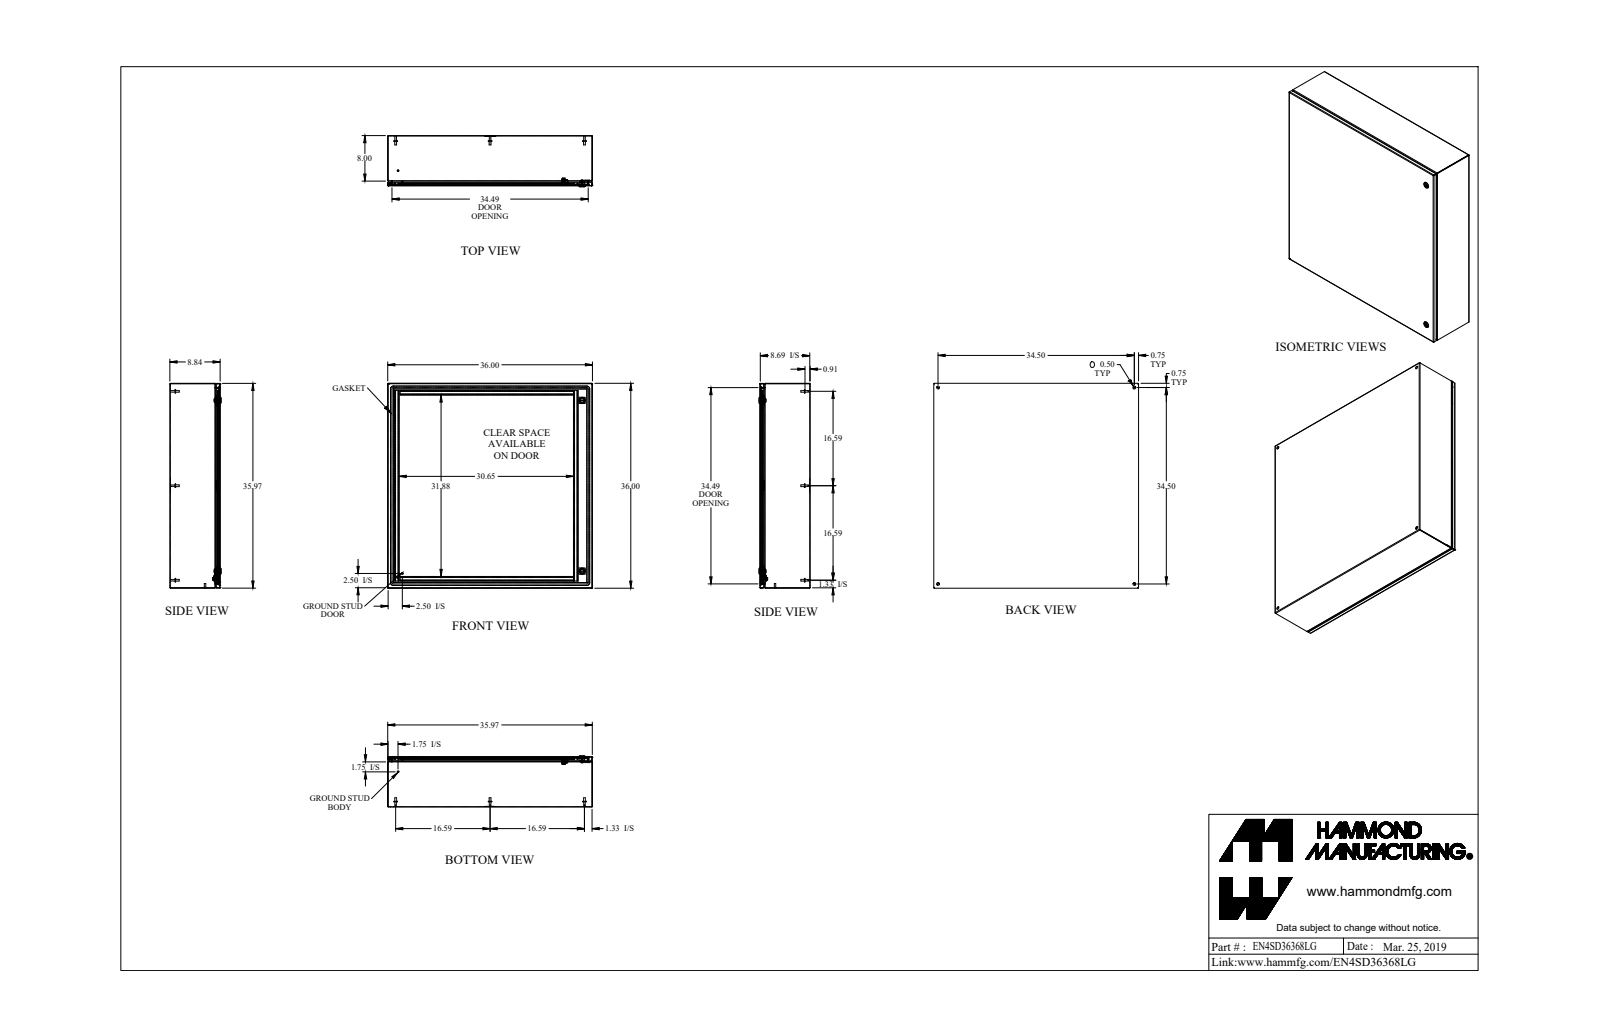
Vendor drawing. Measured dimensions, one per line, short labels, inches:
name: EN4SD36368LG_Default
written by: SolidWorks 2019 (CONFIG_CONTROL_DESIGN)
unit: in
bodies: 41 solids, 1184 faces (555 planar, 394 cylindrical, 235 other)
size: 36 × 36 × 8.997
volume: 313.8 in³; area: 8 875 in²
holes: 4× ⌀0.5, 2× ⌀0.232, 2× ⌀0.625, 2× ⌀0.785, 1× ⌀0.172, 1× ⌀0.196, 1× ⌀0.24, 1× ⌀0.242, 1× ⌀0.275, 1× ⌀0.375
bosses: 8× ⌀0.313, 8× ⌀0.27, 7× ⌀0.625, 2× ⌀1.1, 2× ⌀0.625, 2× ⌀0.525, 2× ⌀0.281, 2× ⌀0.25
rounds: 24× R0.043, 24× R0.081, 20× R0.036, 20× R0.108, 14× R0.062, 10× R0.094, 10× R0.312, 9× R0.016
face distances: 0.072, 8.765, 8.693, 8.837, 35.928, 35.856, 36, 7.928, 0.837, 0.038
hole spacings: 34.5, 33.503, 48.791, 2.493, 2.494, 3.542, 4.441, 29.999
